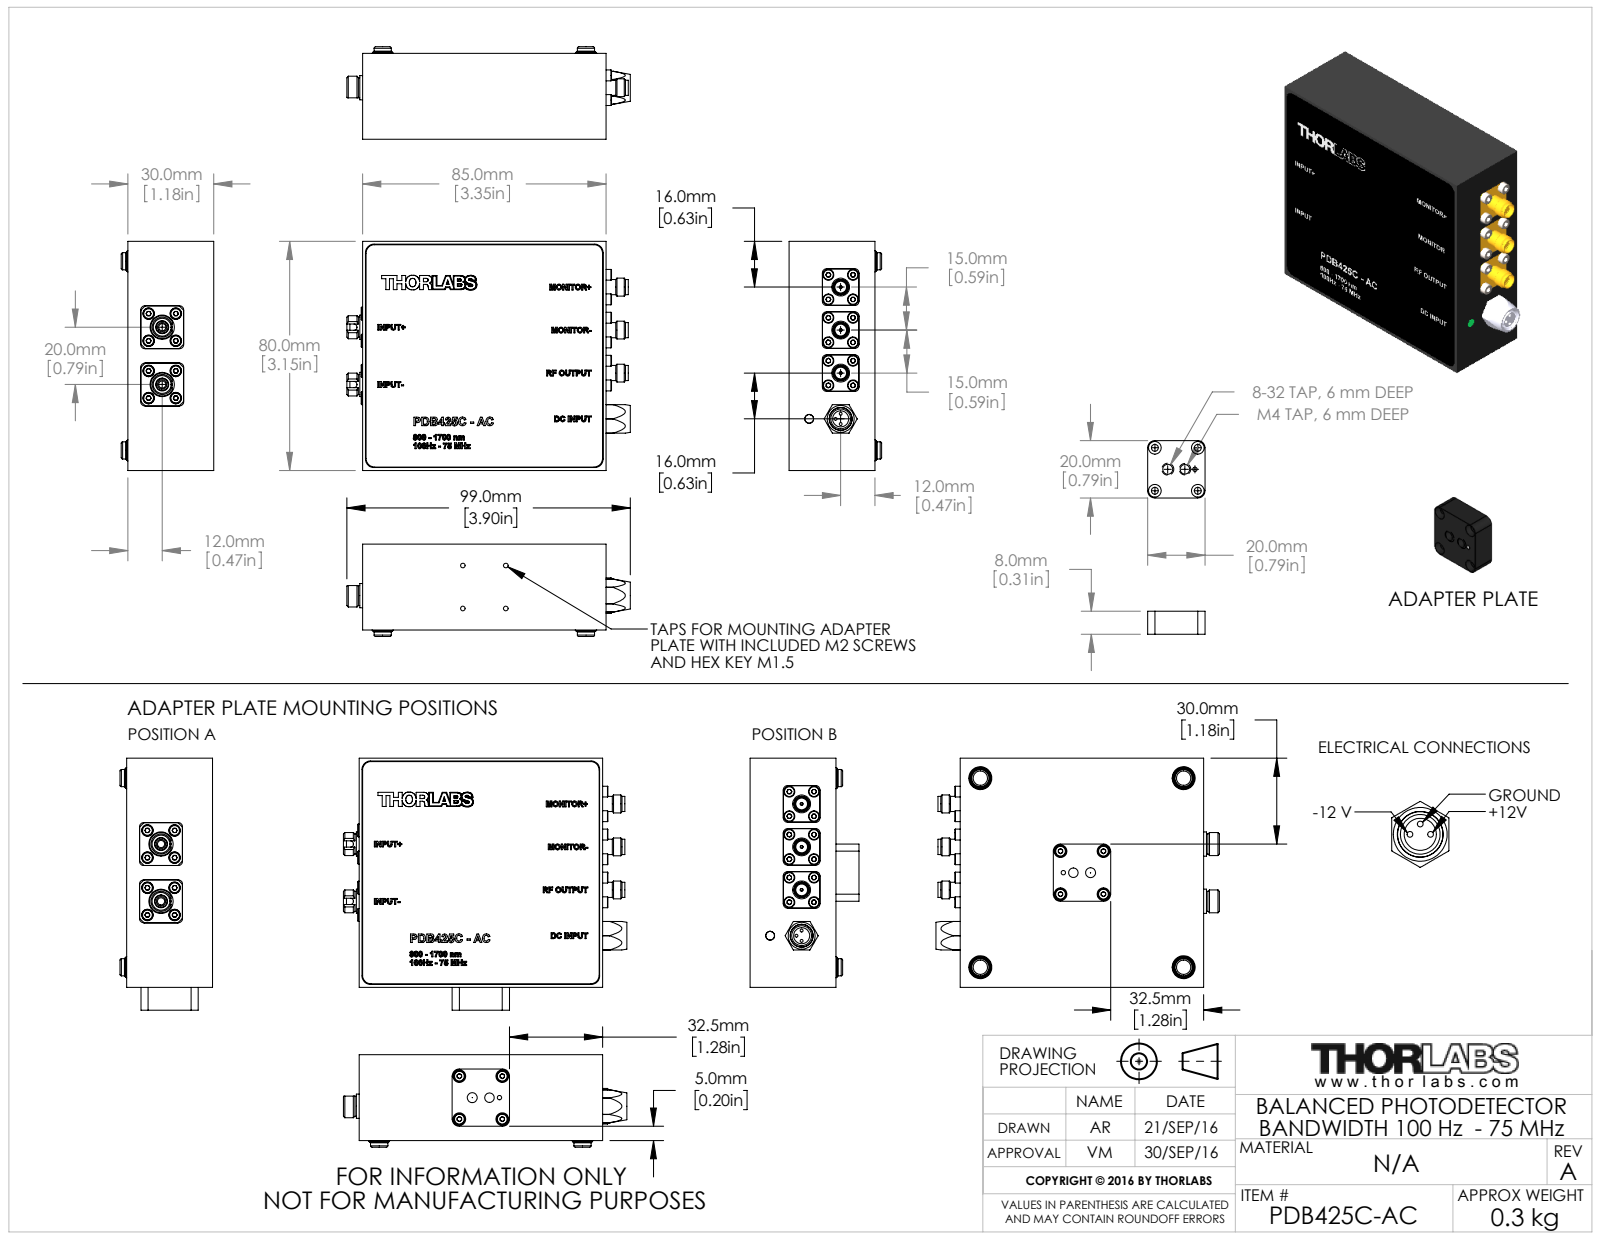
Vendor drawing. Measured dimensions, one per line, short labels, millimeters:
name: MTN005464-E0W
written by: SolidWorks 2014 (AUTOMOTIVE_DESIGN)
unit: mm
bodies: 90 solids, 3079 faces (1792 planar, 584 cylindrical, 703 other)
size: 99 × 88 × 38
volume: 87 719 mm³; area: 57 809 mm²
holes: 38× ⌀1.6, 12× ⌀2.6, 8× ⌀2.2, 8× ⌀2.4, 8× ⌀4, 8× ⌀4.4, 6× ⌀1.02, 5× ⌀8, 3× ⌀0.8, 3× ⌀1, 3× ⌀4.1, 3× ⌀4.2
bosses: 20× ⌀3.8, 20× ⌀2, 8× ⌀4.5, 8× ⌀2.5, 6× ⌀0.43, 4× ⌀6, 3× ⌀6.22, 3× ⌀5.3
rounds: 20× R1.5, 12× R3, 8× R2.5, 8× R5, 4× R1, 2× R9.5, 1× R5.75
face distances: 29.7, 6, 23.7, 5.5, 80, 2, 74.5, 85, 3.5, 83
hole spacings: 15, 6.08, 8.6, 9.5, 6.72, 8.75, 11.53, 12.9
